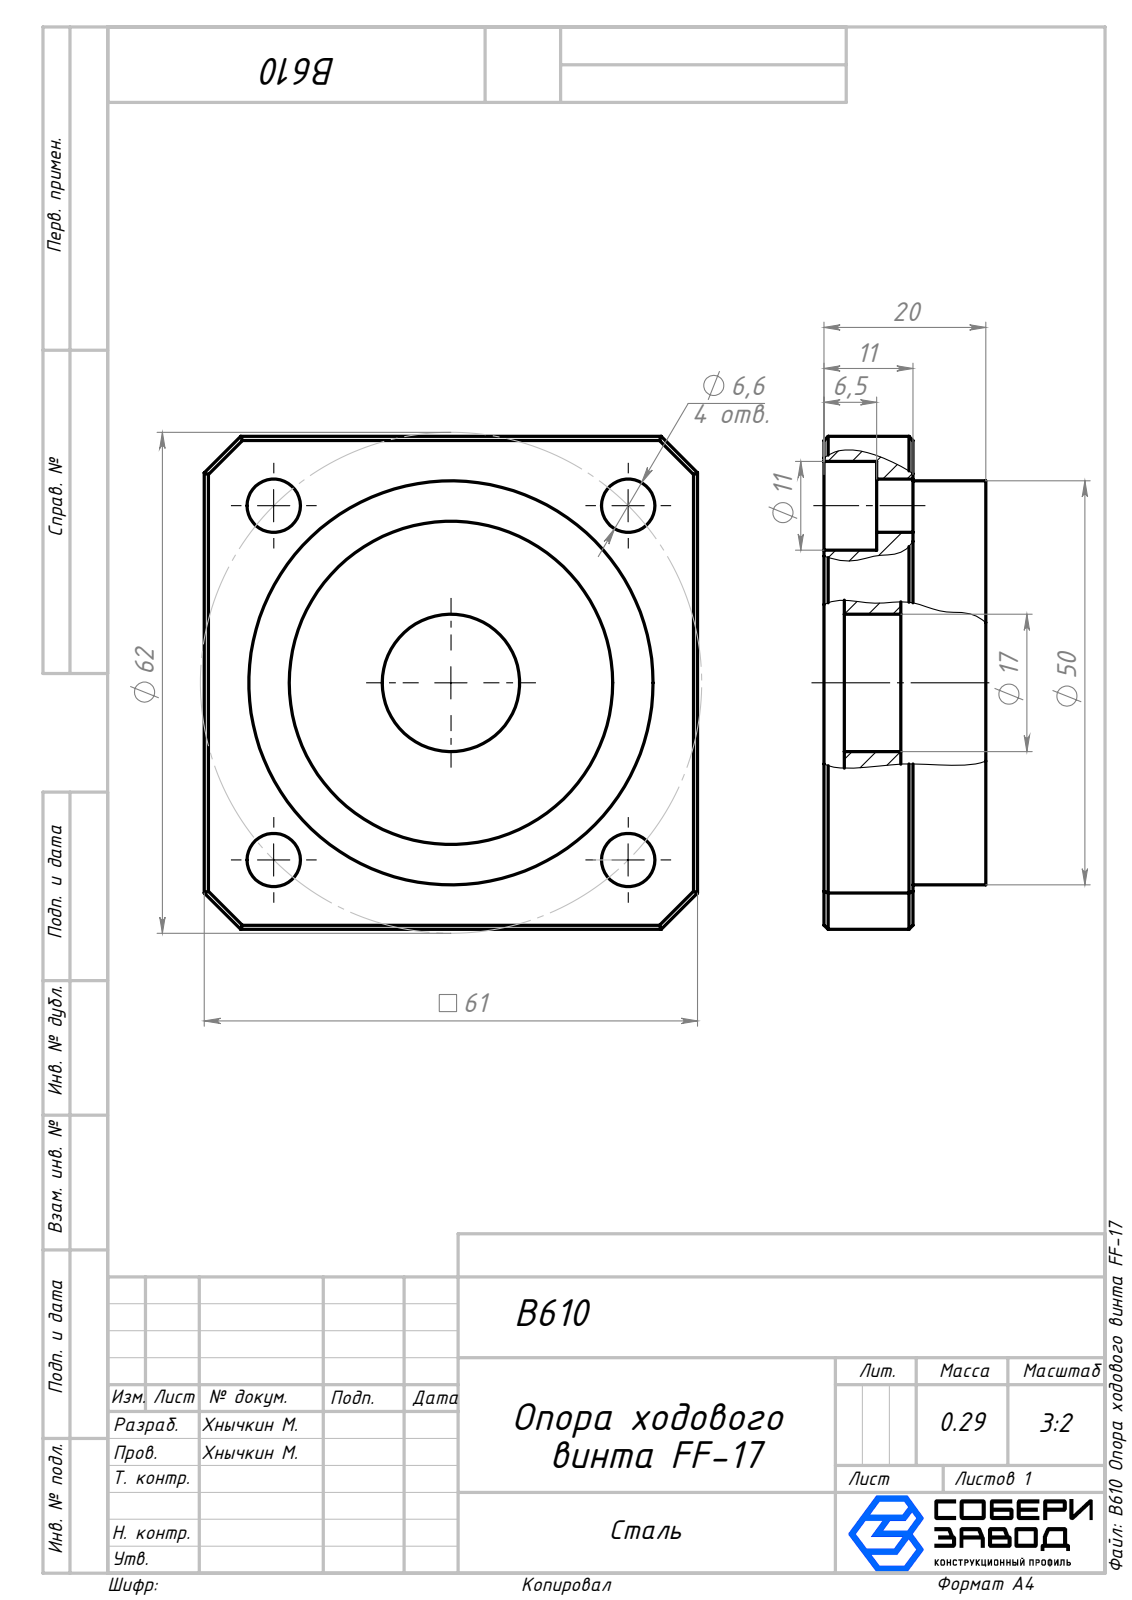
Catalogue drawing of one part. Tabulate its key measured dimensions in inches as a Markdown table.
| quantity | value |
| --- | --- |
| part name | B610 Опора ходового винта FF-17 |
| STEP written by | SolidWorks 2026 (AUTOMOTIVE_DESIGN) |
| units | inches |
| bodies | 2 solids, 57 faces (33 planar, 24 cylindrical, 0 other) |
| overall size | 2.402 × 2.402 × 0.787 |
| volume | 2.263 in³ |
| surface area | 24.05 in² |
| round holes (diameter × count) | 0.26 × 4, 0.433 × 4, 0.669 × 1, 1.575 × 1 |
| round bosses / shafts (diameter × count) | 1.969 × 1 |
| main face-to-face distances | 0.433, 2.402, 0.098, 0.374, 0.276, 0.335, 0.059, 0.787, 0.689, 0.413 |
| hole center spacings | 1.22, 1.726, 2.441 |
